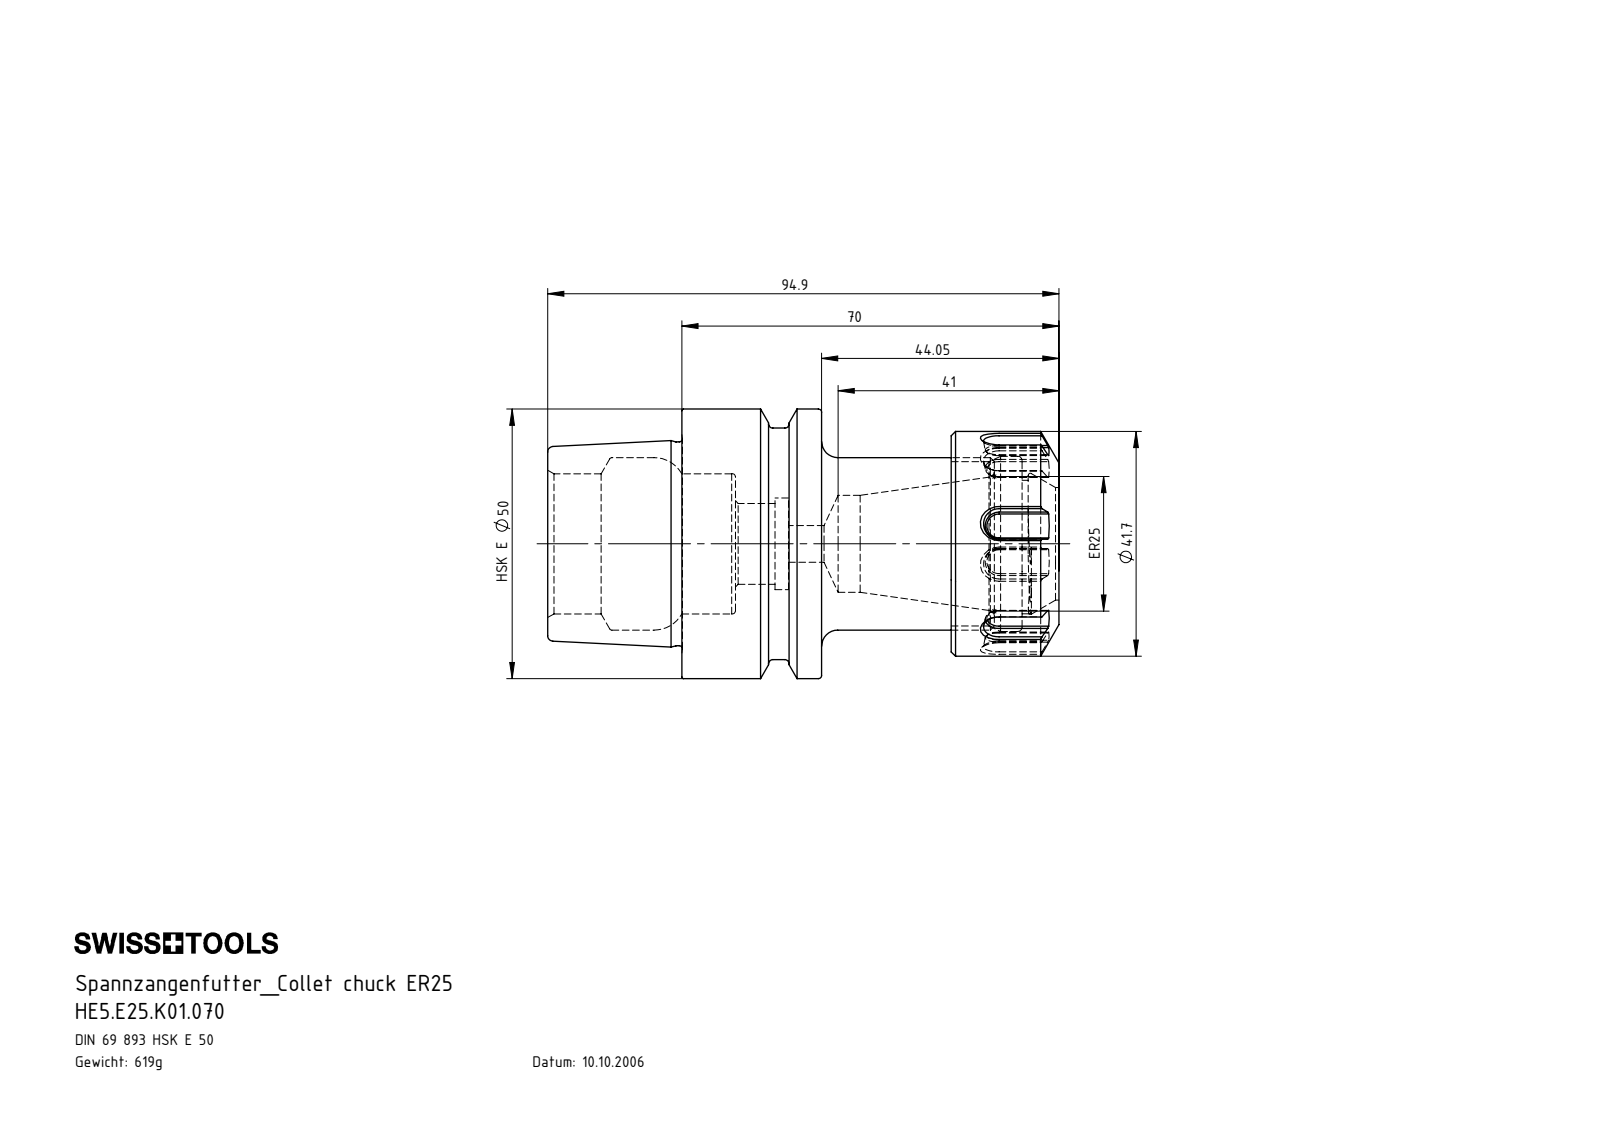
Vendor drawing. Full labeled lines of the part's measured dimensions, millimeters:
Part name (STEP PRODUCT): HE5.E25.K01.070; E25-ER1.001.020; HE5-E25.K01.070_A_Fertigbearbeitung
STEP written by: SolidWorks 2017 (CONFIG_CONTROL_DESIGN)
Units: millimetres
Bodies: 2 solids, 172 faces (59 planar, 35 cylindrical, 78 other)
Overall size (bounding box): 94.9 × 50 × 50
Volume: 78 917 mm³ · Surface area: 26 159 mm²
Round holes (diameter × count): ⌀6.8 ×1, ⌀15 ×1, ⌀17 ×1, ⌀18 ×1, ⌀20.9 ×1, ⌀26 ×1, ⌀30.5 ×1, ⌀32 ×1, ⌀32.5 ×1
Round bosses / shafts (diameter × count): ⌀50 ×1, ⌀42.95 ×1, ⌀41.7 ×1, ⌀37.81 ×1
Partial cylindrical surfaces — rounded edges, fillets, slot ends (radius × count): R12.17 ×2
Main face-to-face distances: 25.95, 50, 24.05, 70, 44.05, 20, 24.9, 50.85, 74.9, 94.9
